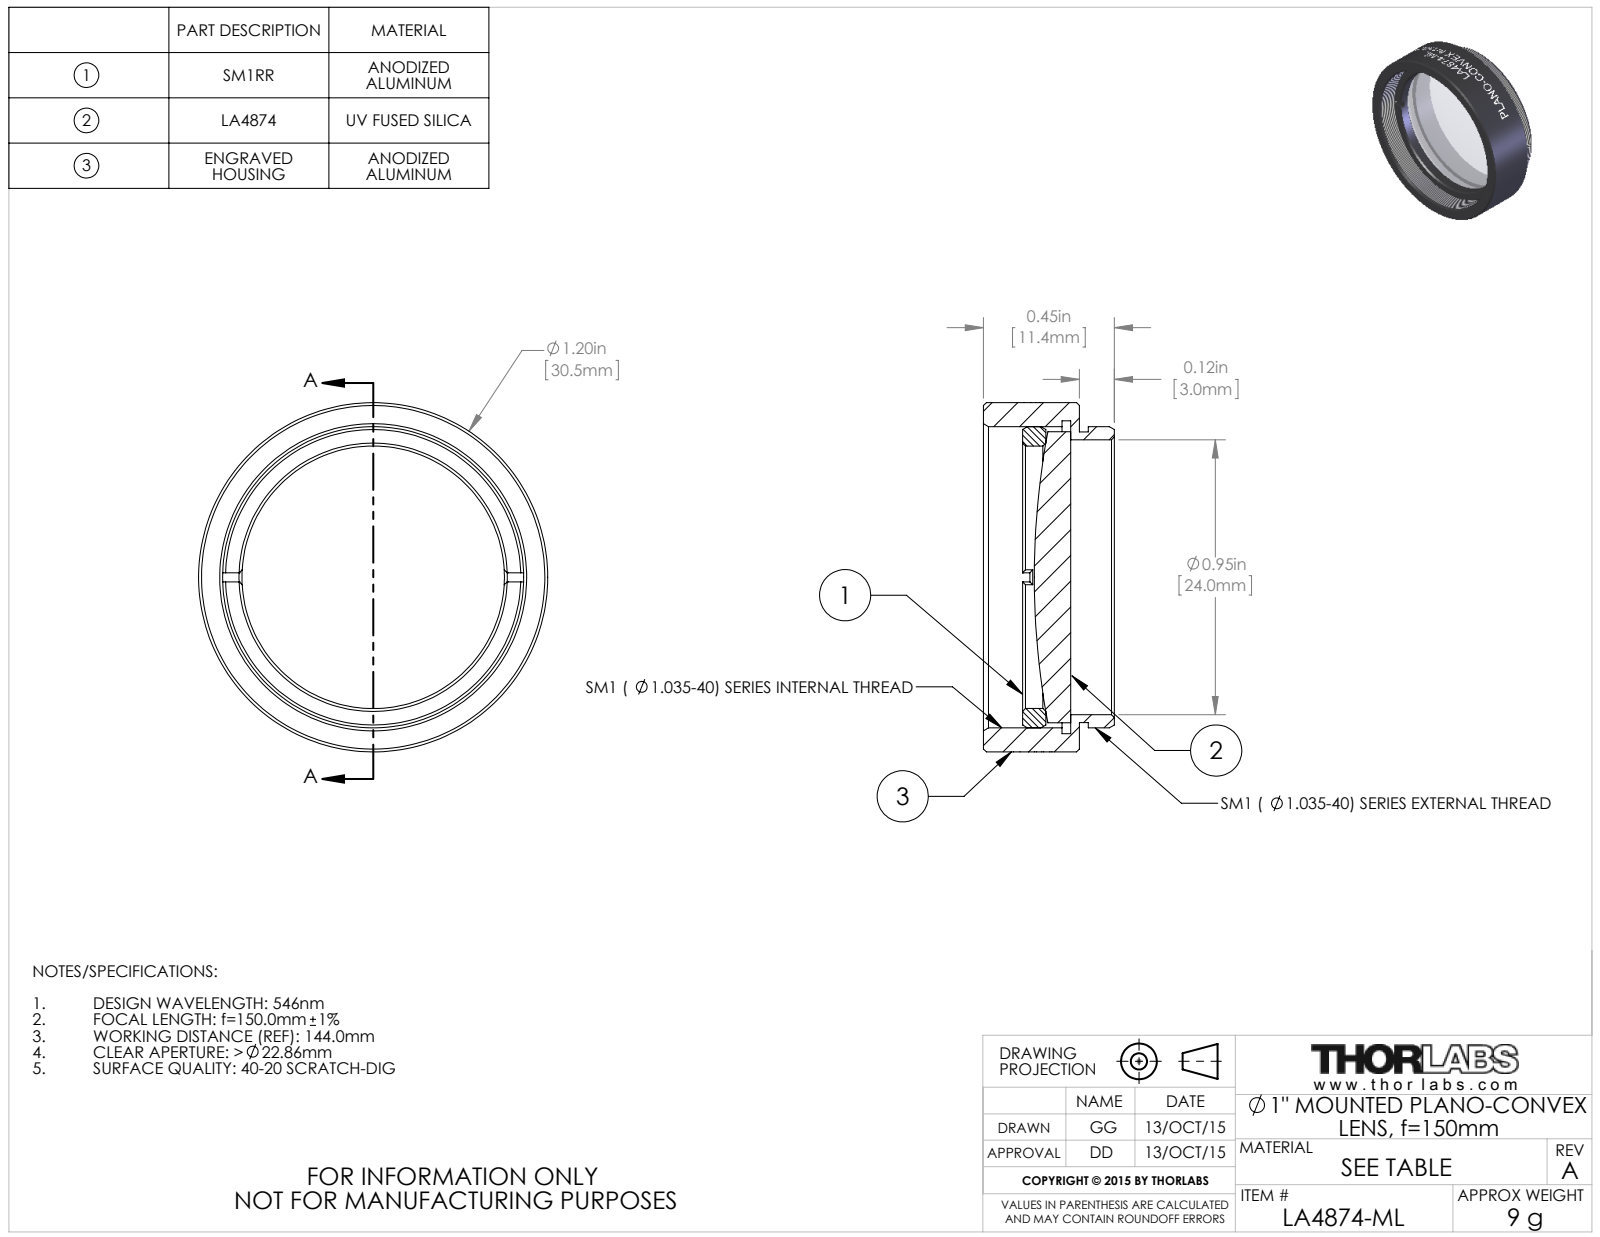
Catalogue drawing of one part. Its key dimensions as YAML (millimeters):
part_name: "TTN039410-E0W"
step_written_by: "SolidWorks 2014 (CONFIG_CONTROL_DESIGN)"
units: millimeters
bodies: {solids: 3, faces: 124, planar: 20, cylindrical: 80, other: 24}
overall_size: [30.48, 30.48, 11.43]
volume: 3394
surface_area: 4317
round_holes:
  - {diameter: 22.91, count: 1}
  - {diameter: 24, count: 1}
  - {diameter: 27.31, count: 1}
round_bosses_or_shafts:
  - {diameter: 30.48, count: 1}
  - {diameter: 26.29, count: 1}
  - {diameter: 25.4, count: 1}
  - {diameter: 25.37, count: 1}
face_to_face_distances: [0.76, 8.38, 7.62, 2.94, 2.18, 5.44, 4.98, 4.22, 2.04, 3.4]
